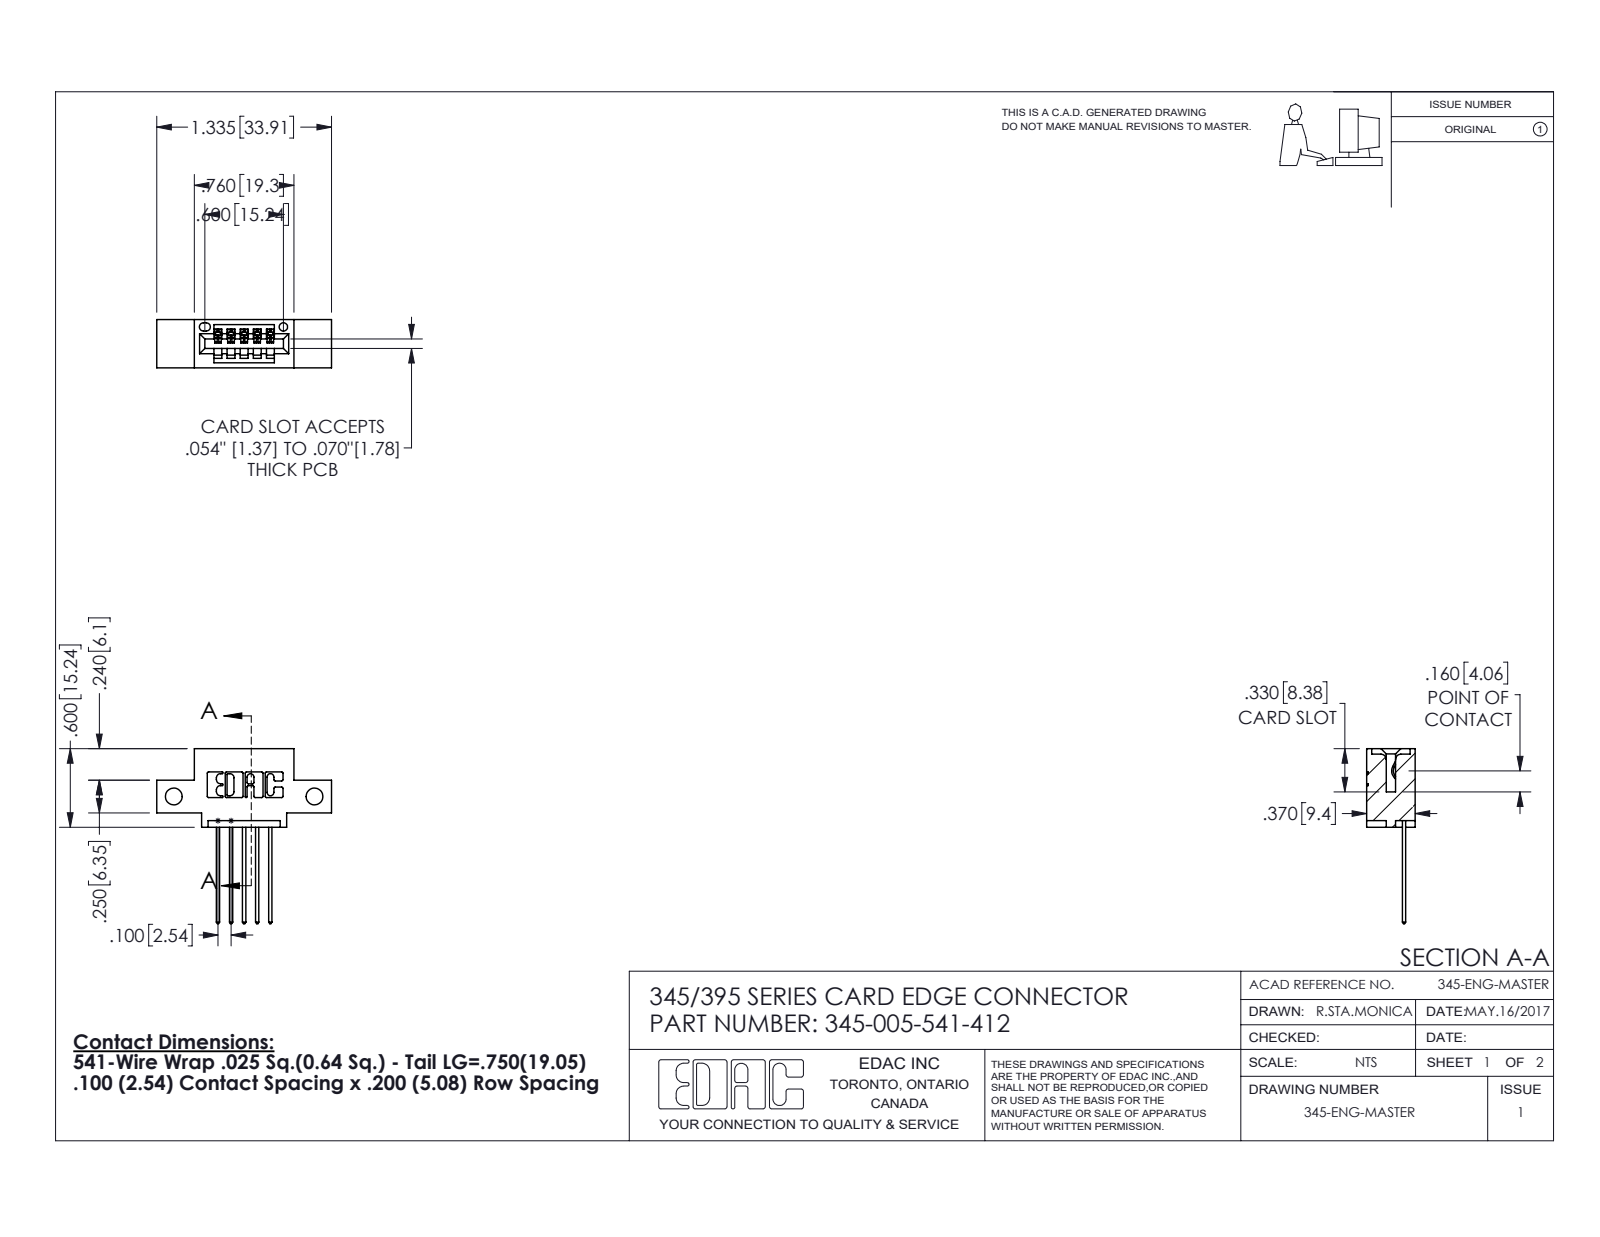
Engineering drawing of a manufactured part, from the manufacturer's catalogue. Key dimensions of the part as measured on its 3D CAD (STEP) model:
Part name (STEP PRODUCT): 345-005-541-412; 345-292-001_345-293-141; 345 Part_0.110 Offset - Side Mount
STEP written by: SolidWorks 2016 (CONFIG_CONTROL_DESIGN)
Units: inches
Bodies: 6 solids, 420 faces (284 planar, 136 cylindrical, 0 other)
Overall size (bounding box): 1.337 × 1.335 × 0.37
Volume: 0.169 in³ · Surface area: 4.991 in²
Round holes (diameter × count): ⌀0.128 ×2, ⌀0.064 ×1
Partial cylindrical surfaces — rounded edges, fillets, slot ends (radius × count): R0.01 ×22, R0.006 ×10, R0.01 ×10, R0.007 ×6, R0.031 ×6, R0.026 ×3, R0.031 ×2, R0.04 ×2
Main face-to-face distances: 0.2, 0.37, 0.298, 0.072, 0.1, 0.025, 0.098, 0.272, 0.25, 0.06
Hole centre spacings: 1.075
